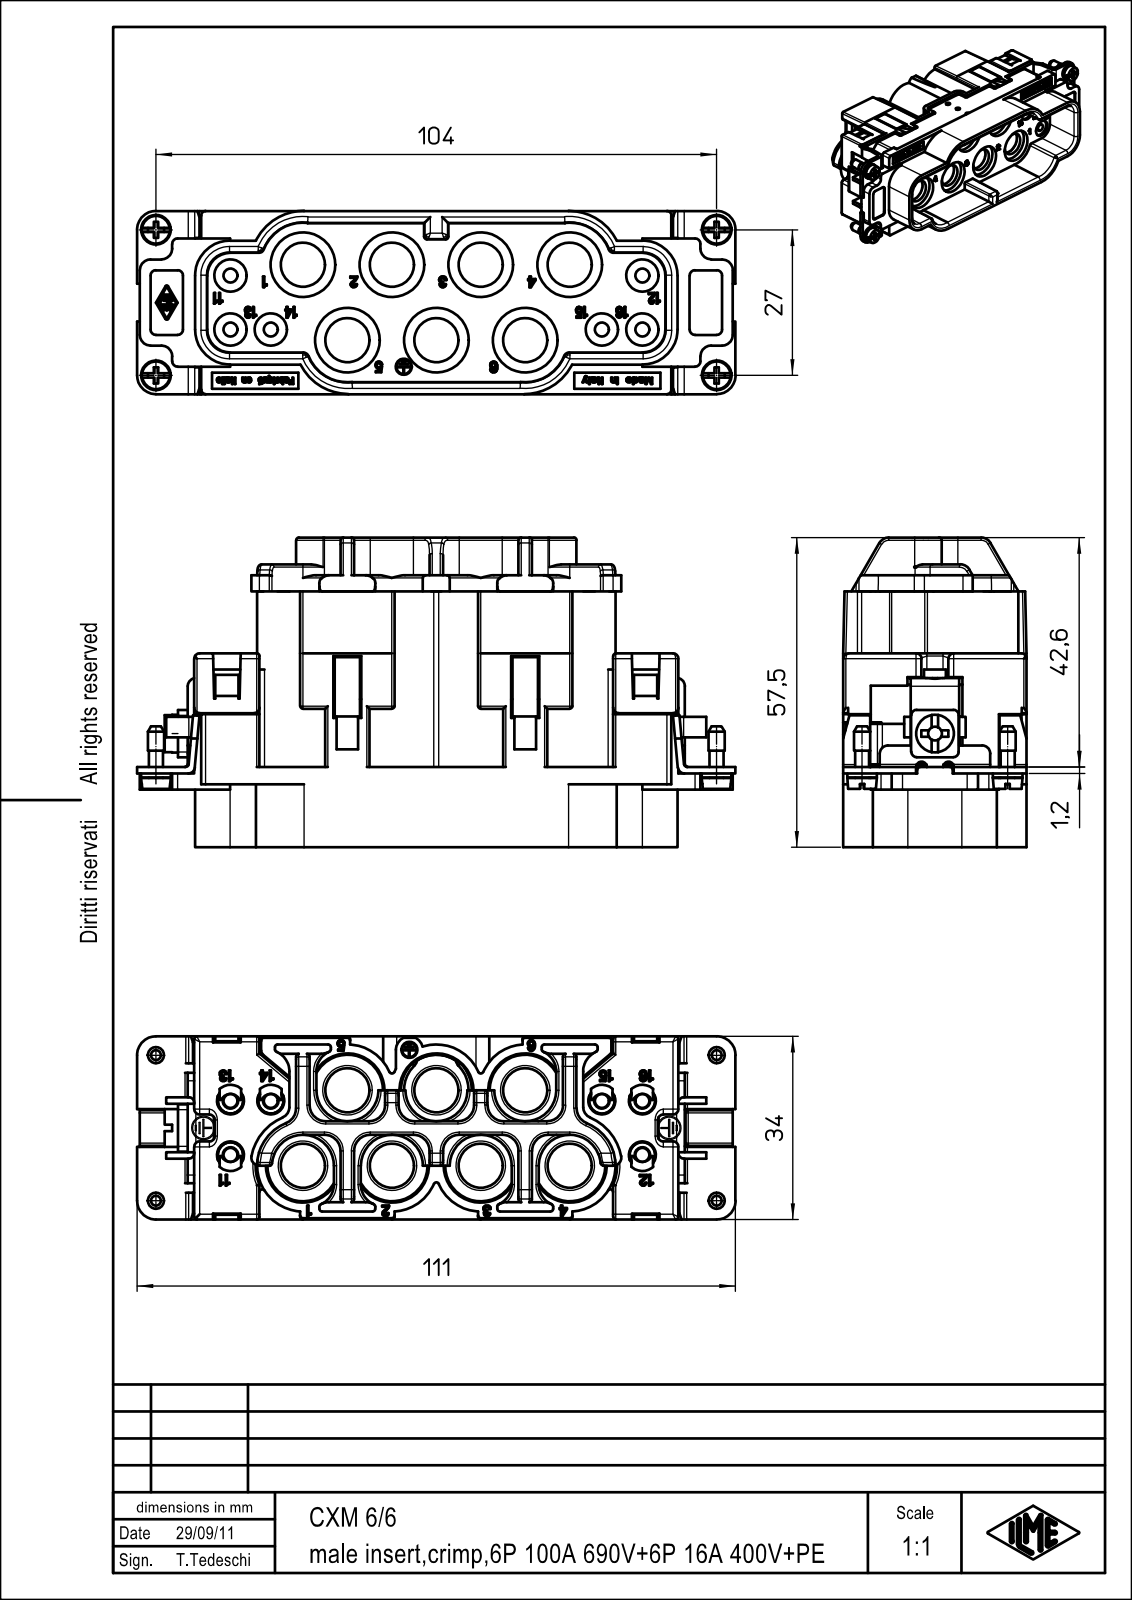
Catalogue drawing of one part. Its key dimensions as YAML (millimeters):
part_name: "CXM_6-6"
step_written_by: "PTC Creo Elements/Direct Modeling 19.0E 27-Jun-2016 (C) Parametric Technology GmbH (AUTOMOTIVE_DESIGN)"
units: millimeters
bodies: {solids: 1, faces: 2480, planar: 1978, cylindrical: 396, other: 106}
overall_size: [111, 57.5, 34.4]
volume: 99503
surface_area: 40891
round_holes:
  - {diameter: 8, count: 7}
  - {diameter: 2.8, count: 4}
  - {diameter: 1.6, count: 2}
  - {diameter: 2.58, count: 1}
round_bosses_or_shafts:
  - {diameter: 2.48, count: 6}
  - {diameter: 5.5, count: 4}
  - {diameter: 3, count: 4}
  - {diameter: 2.6, count: 4}
  - {diameter: 15, count: 1}
  - {diameter: 7, count: 1}
  - {diameter: 5, count: 1}
  - {diameter: 4, count: 1}
partial_cylinders:
  - {radius: 0.5, count: 82}
  - {radius: 1, count: 33}
  - {radius: 3, count: 24}
  - {radius: 0.4, count: 16}
  - {radius: 0.2, count: 11}
  - {radius: 2, count: 11}
  - {radius: 2.5, count: 9}
  - {radius: 5.75, count: 7}
face_to_face_distances: [34, 1.2, 5.5, 11.5, 1.4, 1.5, 0.8, 3, 22.3, 2]
hole_center_spacings: [16.25, 16.5, 28.44, 33, 27, 28.01, 34.1, 36.09]
